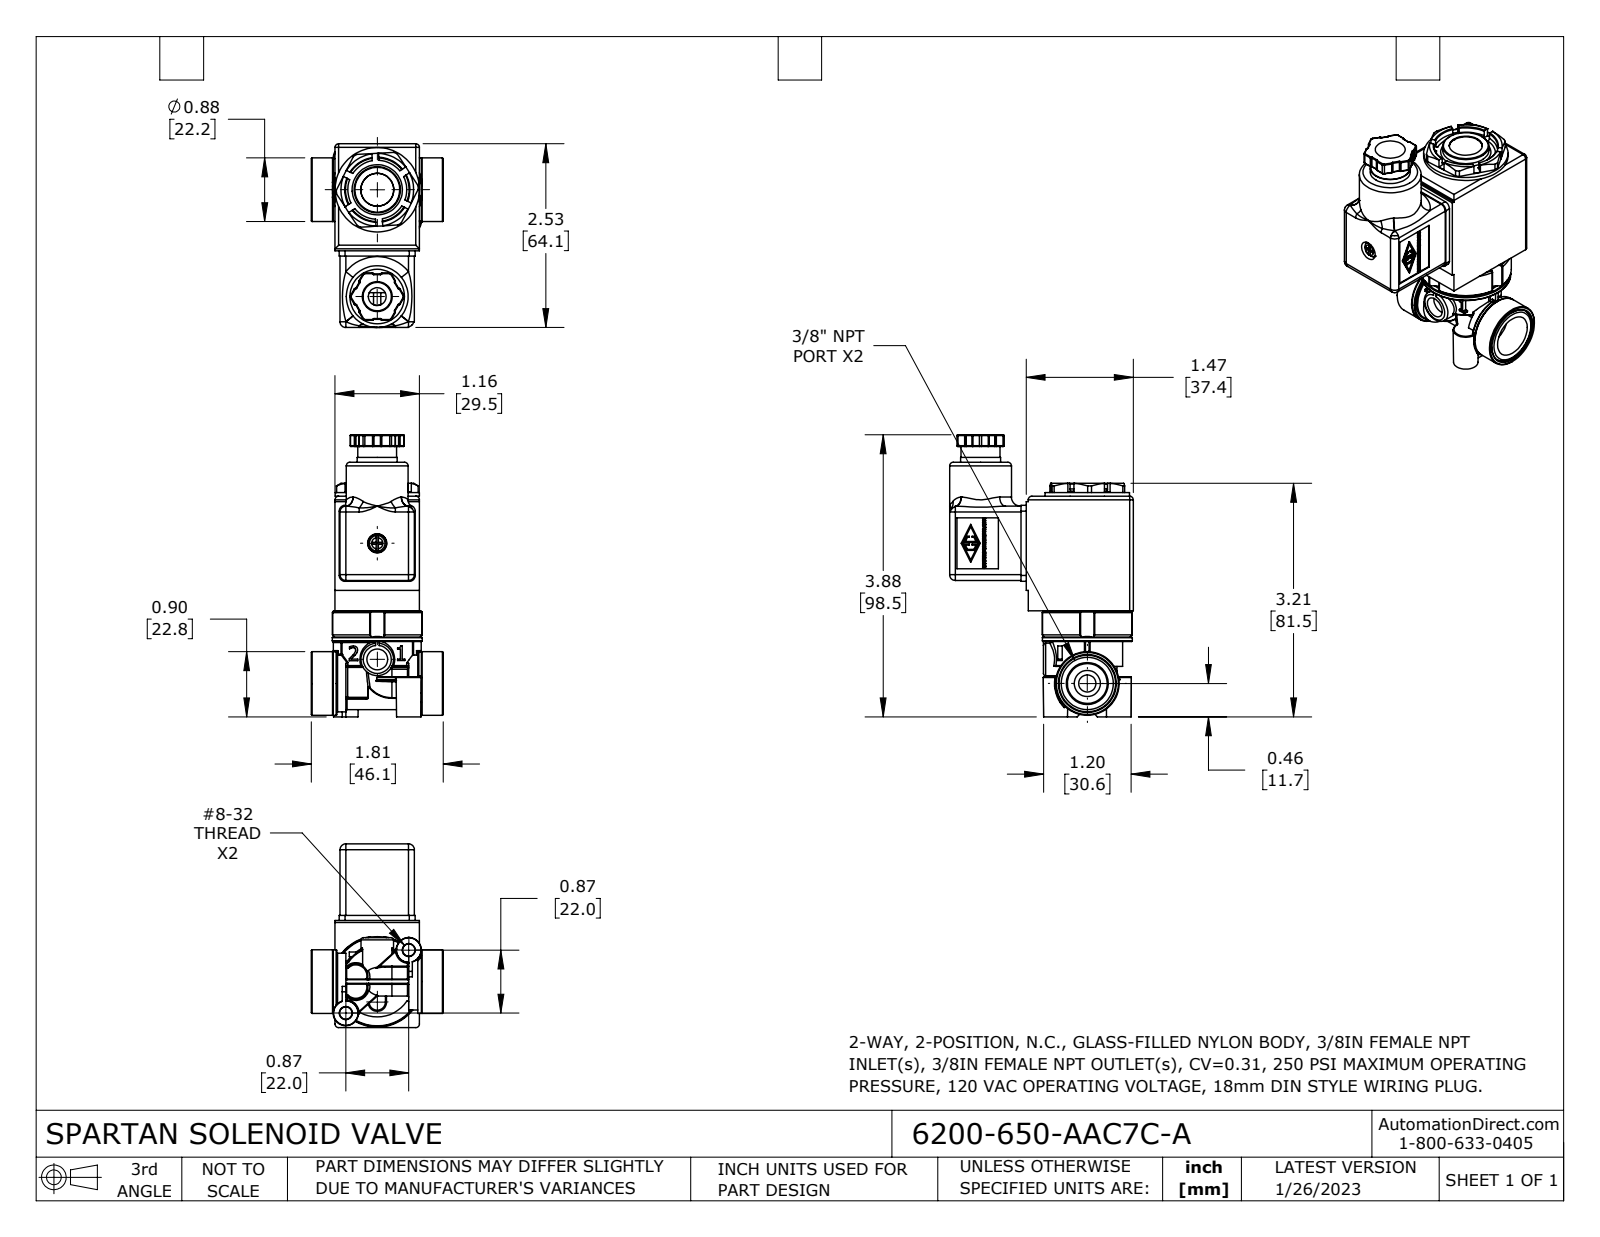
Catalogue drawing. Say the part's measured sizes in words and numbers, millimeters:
The part is named "6200-650-AAC7C-A". Its 3-D file was written by "SolidWorks 2021 (CONFIG_CONTROL_DESIGN)". It is 3 solids with 4462 faces: 805 planar, 3033 cylindrical and 624 other. Overall it measures 98.5 by 64.2 by 46.1 millimeters. Its volume is 71 550 cubic millimeters and its surface area 35 830 square millimeters. Round holes: 2 of diameter 6, 1 of diameter 1.3, 1 of diameter 1.5, 1 of diameter 2.4, 1 of diameter 2.6, 1 of diameter 3, 1 of diameter 5.2, 1 of diameter 6.2, 1 of diameter 6.4, 1 of diameter 6.7, 1 of diameter 7.3, 1 of diameter 9.9. Round bosses or shafts: 58 of diameter 0.2, 1 of diameter 31.4, 1 of diameter 29.5, 1 of diameter 25.4, 1 of diameter 24.7, 1 of diameter 22.2, 1 of diameter 22.2, 1 of diameter 21.6. Partial cylindrical surfaces (rounded edges, fillets, slot ends): 68 of radius 0.3, 34 of radius 0.4, 14 of radius 1.3, 12 of radius 2, 6 of radius 0.8, 4 of radius 0.2, 4 of radius 0.5, 4 of radius 1. The main face-to-face distances are 29.5, 23.5, 2, 26.5, 23.3, 1.2, 24.7, 2, 3, 26.5. The hole center spacings are 7.1, 8.7, 28.6, 35.8, 37.3, 40.5, 44.5, 56.2.
